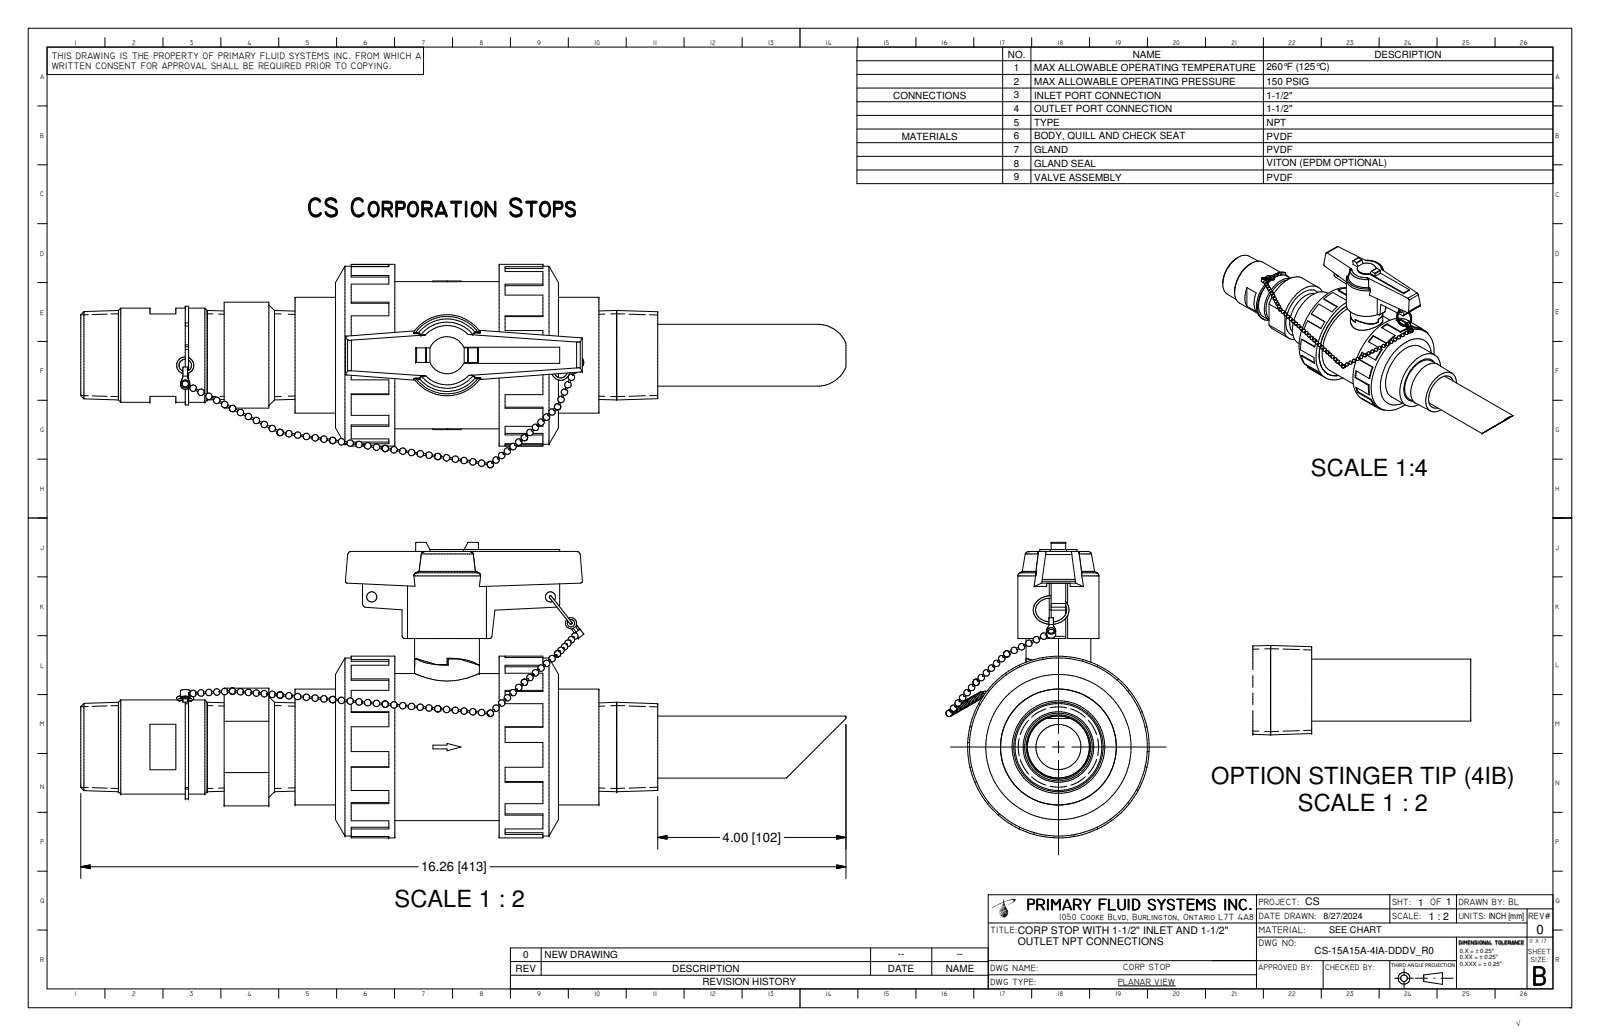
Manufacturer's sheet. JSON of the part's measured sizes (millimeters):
{"step_written_by": "Autodesk Inventor 2025 (CONFIG_CONTROL_DESIGN)", "units": "millimeters", "bodies": {"solids": 19, "faces": 532, "planar": 301, "cylindrical": 131, "other": 100}, "overall_size": [413, 159.4, 109.7], "volume_mm3": 1052000, "surface_area_mm2": 260100, "round_holes": [[2.5, 2], [3.8, 2], [4, 2], [5.5, 2], [24.3, 1], [26.6, 1], [34.7, 1], [38.1, 1], [40, 1], [45.8, 1], [48.3, 1], [50, 1]], "round_bosses_or_shafts": [[0.9, 9], [6, 2], [98, 1], [96, 1], [88.2, 1], [79.3, 1], [62.5, 1], [50.8, 1]], "partial_cylinders_radius": [[0.5, 4], [2, 4], [1, 2], [1.2, 2], [1.5, 2], [2.5, 2], [5, 2], [10, 1]], "face_to_face_distances": [25.4, 81.8, 107.2, 25.4, 81.8, 6.6, 6.6, 32, 88.4, 113.8], "hole_center_spacings": [8, 11, 18, 19, 25.5, 25.5, 28.8, 96.5]}
